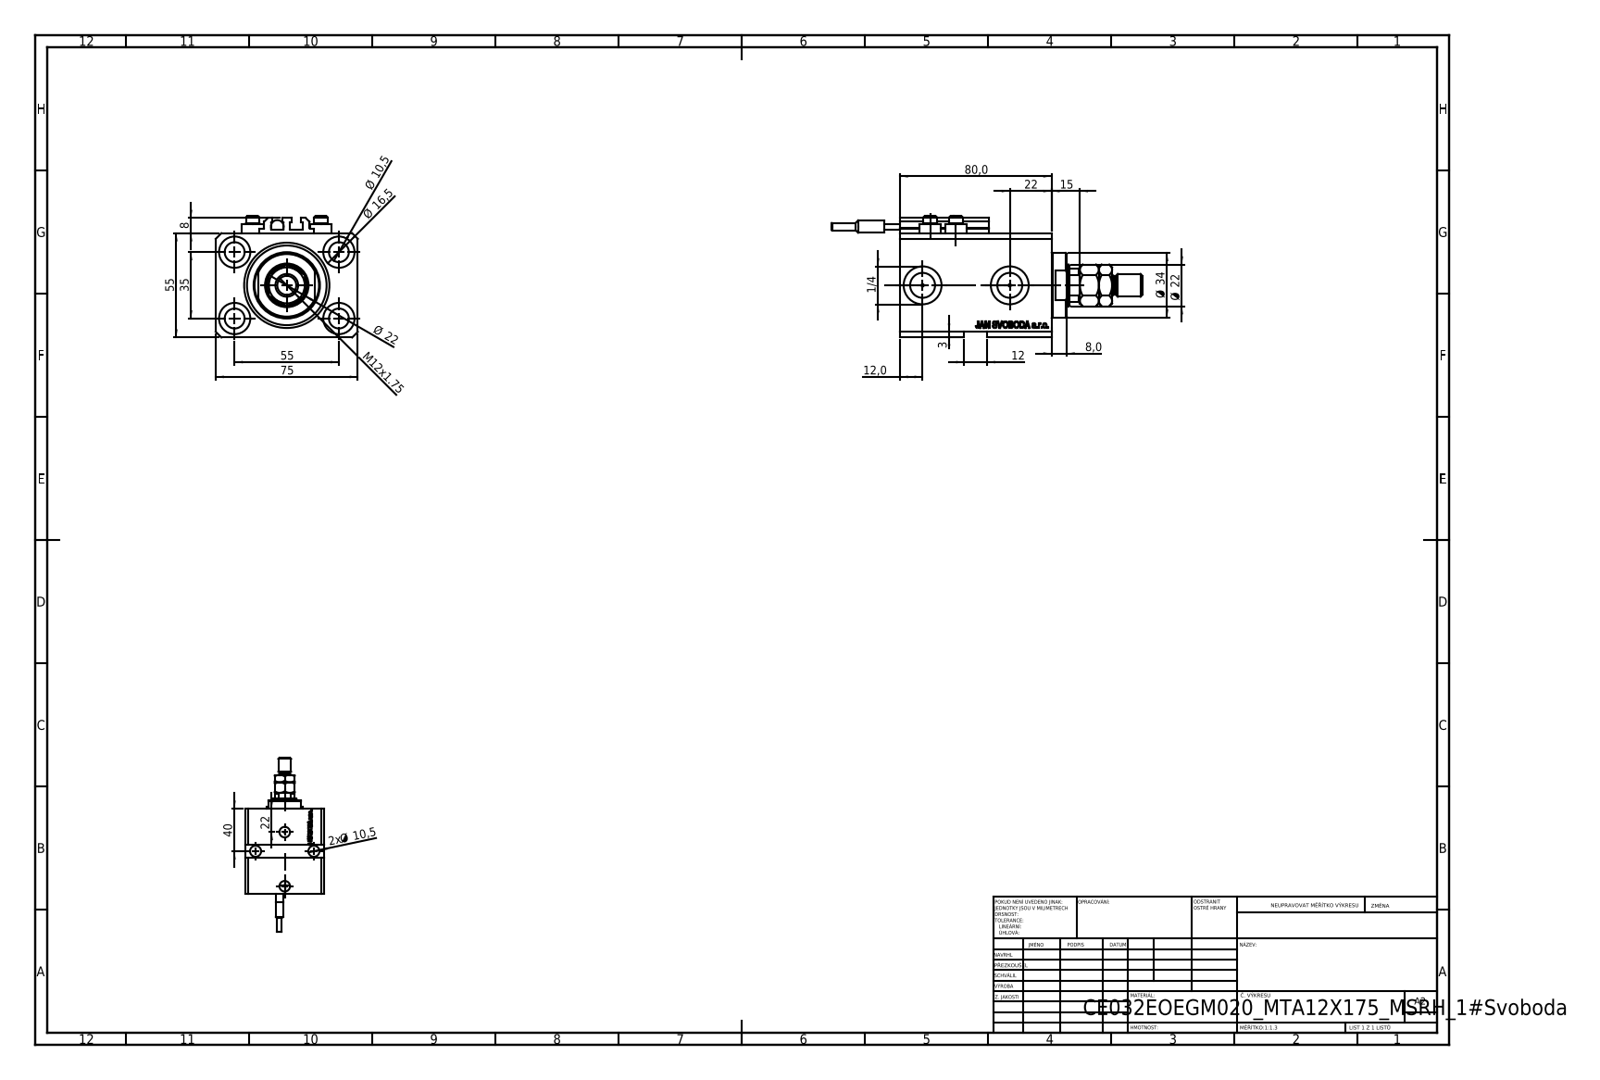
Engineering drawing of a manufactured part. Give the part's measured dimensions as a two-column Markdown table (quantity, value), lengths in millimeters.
| quantity | value |
| --- | --- |
| part name | V250CE_E_Body; MTA; SWITCH_V250CE; V250CE_VC_E (+2 more) |
| STEP written by | SolidWorks 2019 (CONFIG_CONTROL_DESIGN) |
| units | millimeters |
| bodies | 10 solids, 1139 faces (545 planar, 136 cylindrical, 458 other) |
| overall size | 164 × 75 × 64 |
| volume | 292 656 mm³ |
| surface area | 78 156 mm² |
| round holes (diameter × count) | 10.5 × 7, 1.25 × 4, 4 × 4, 16.5 × 4, 10 × 2, 13.16 × 2, 20 × 2, 22 × 1, 32 × 1, 45 × 1 |
| round bosses / shafts (diameter × count) | 11.6 × 4, 7 × 4, 34 × 1, 12 × 1, 10 × 1, 6.8 × 1, 6.5 × 1, 4 × 1 |
| partial cylindrical surfaces (radius × count) | 0.2 × 10, 10.5 × 1 |
| main face-to-face distances | 55, 75, 15, 65, 80, 3, 55.1, 9.9, 70.1, 54 |
| hole center spacings | 32.6, 55, 13.6, 14.09, 19.89, 20.12, 25.81, 28.48 |
